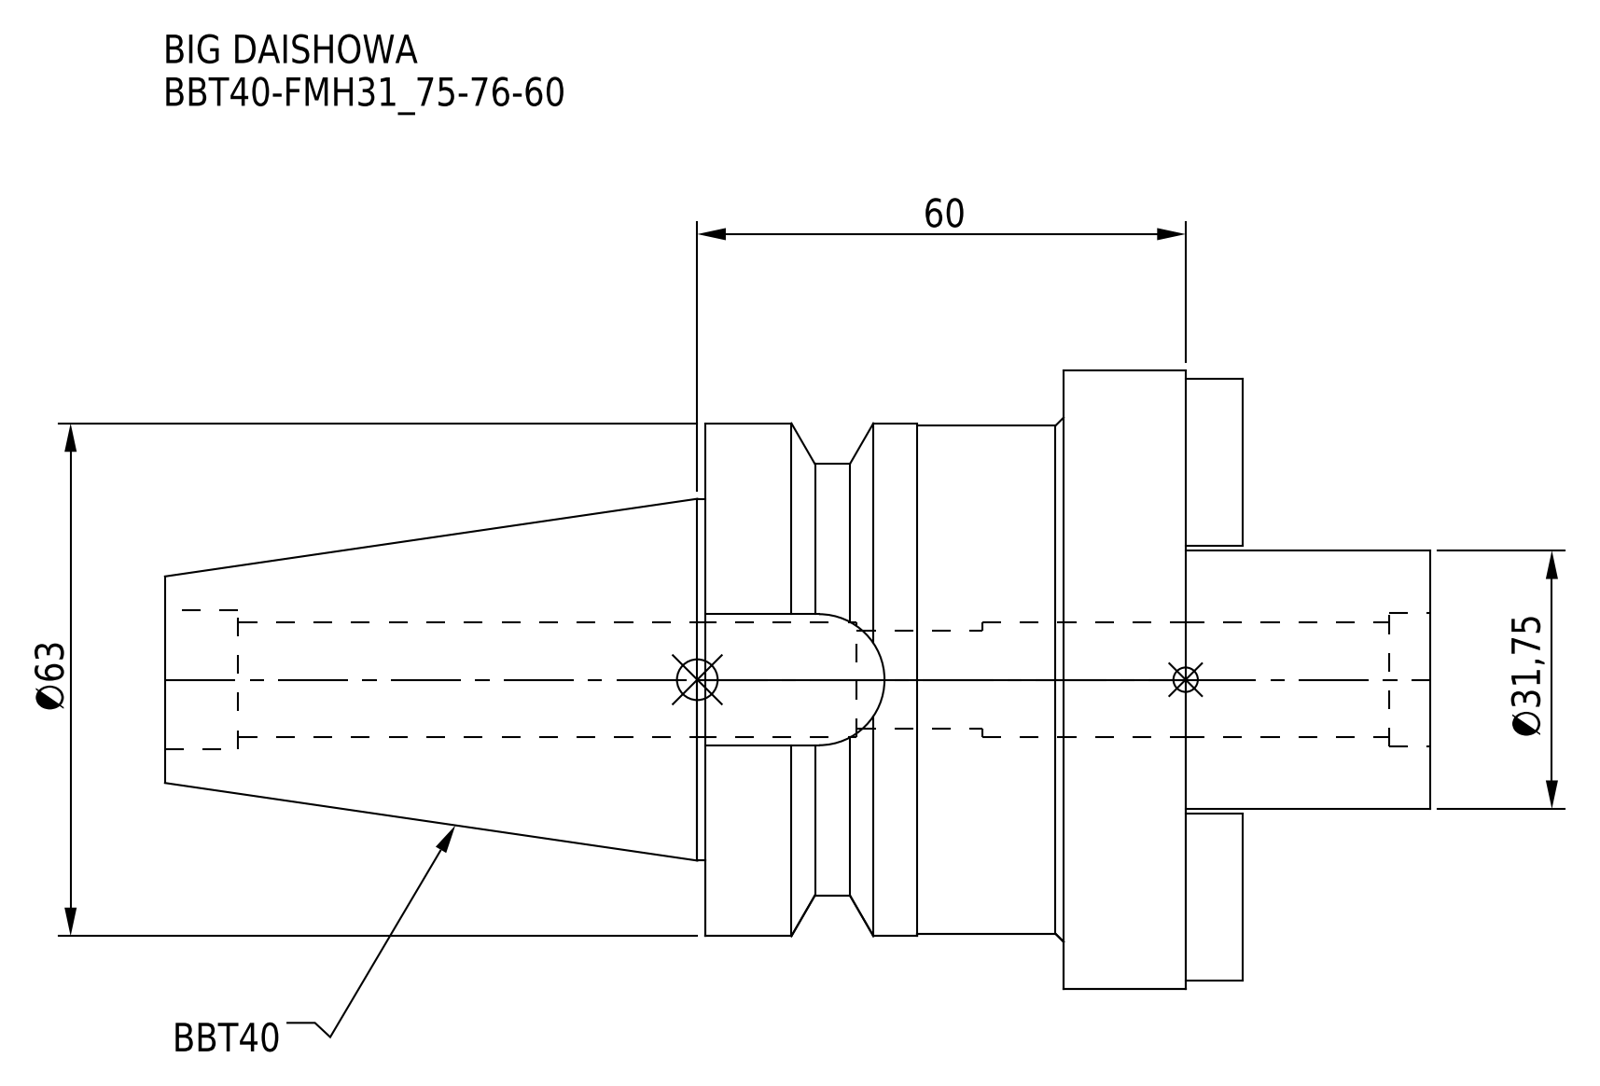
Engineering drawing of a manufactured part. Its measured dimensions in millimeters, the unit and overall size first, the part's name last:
Units: millimetres
Overall size (bounding box): 155.4 × 76 × 76
Round holes (diameter × count): ⌀12 ×1, ⌀14 ×1, ⌀14.2 ×1, ⌀16.5 ×1, ⌀17 ×1
Round bosses / shafts (diameter × count): ⌀76 ×1, ⌀63 ×1, ⌀62.4 ×1, ⌀53 ×1, ⌀44.45 ×1, ⌀31.75 ×1
Partial cylindrical surfaces — rounded edges, fillets, slot ends (radius × count): R8.05 ×1
Main face-to-face distances: 59, 15, 44, 45, 30, 89, 16.15, 28.85, 23, 7
Volume: 261 582 mm³ · Surface area: 39 371 mm²
Bodies: 1 solid, 64 faces (26 planar, 30 cylindrical, 8 other)
Part name (STEP PRODUCT): BBT40-FMH31_75-76-60
STEP written by: CREO PARAMETRIC BY PTC INC, 2016380 (AUTOMOTIVE_DESIGN)
